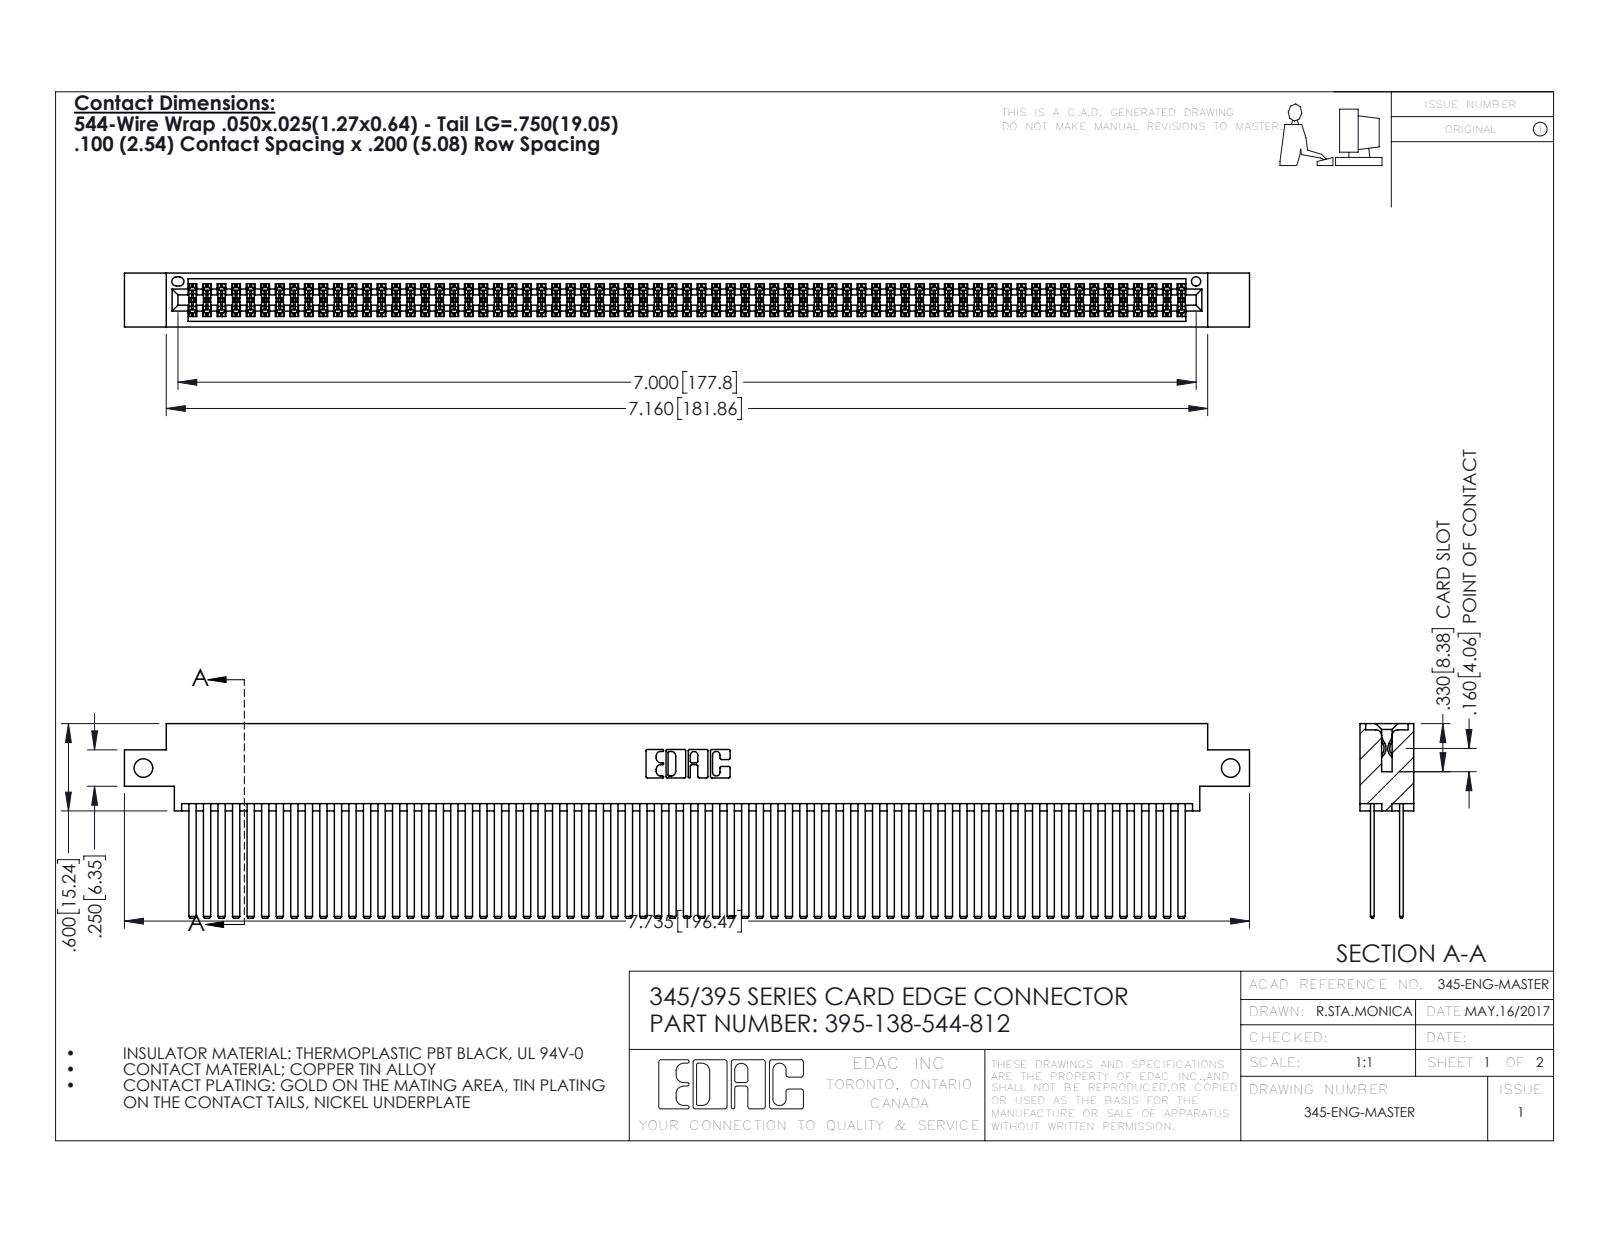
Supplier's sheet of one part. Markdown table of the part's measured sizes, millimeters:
| quantity | value |
| --- | --- |
| part name | 345 Part_0.170 Offset - Side Mount; 345-292-001_345-293-144; 395-138-544-812 |
| STEP written by | SolidWorks 2016 (CONFIG_CONTROL_DESIGN) |
| units | millimeters |
| bodies | 139 solids, 6202 faces (4086 planar, 2116 cylindrical, 0 other) |
| overall size | 196.5 × 34 × 9.4 |
| volume | 21 070 mm³ |
| surface area | 37 350 mm² |
| round holes (diameter × count) | 3.3 × 2, 1.6 × 1 |
| partial cylindrical surfaces (radius × count) | 0.2 × 207, 0.3 × 22, 0.2 × 6, 0.8 × 6, 0.7 × 3, 0.4 × 2, 0.5 × 2, 0.6 × 2 |
| main face-to-face distances | 5.1, 0.6, 7.6, 1.8, 2.5, 6.9, 5.7, 4.4, 9.4, 3.8 |
| hole center spacings | 189.9 |
